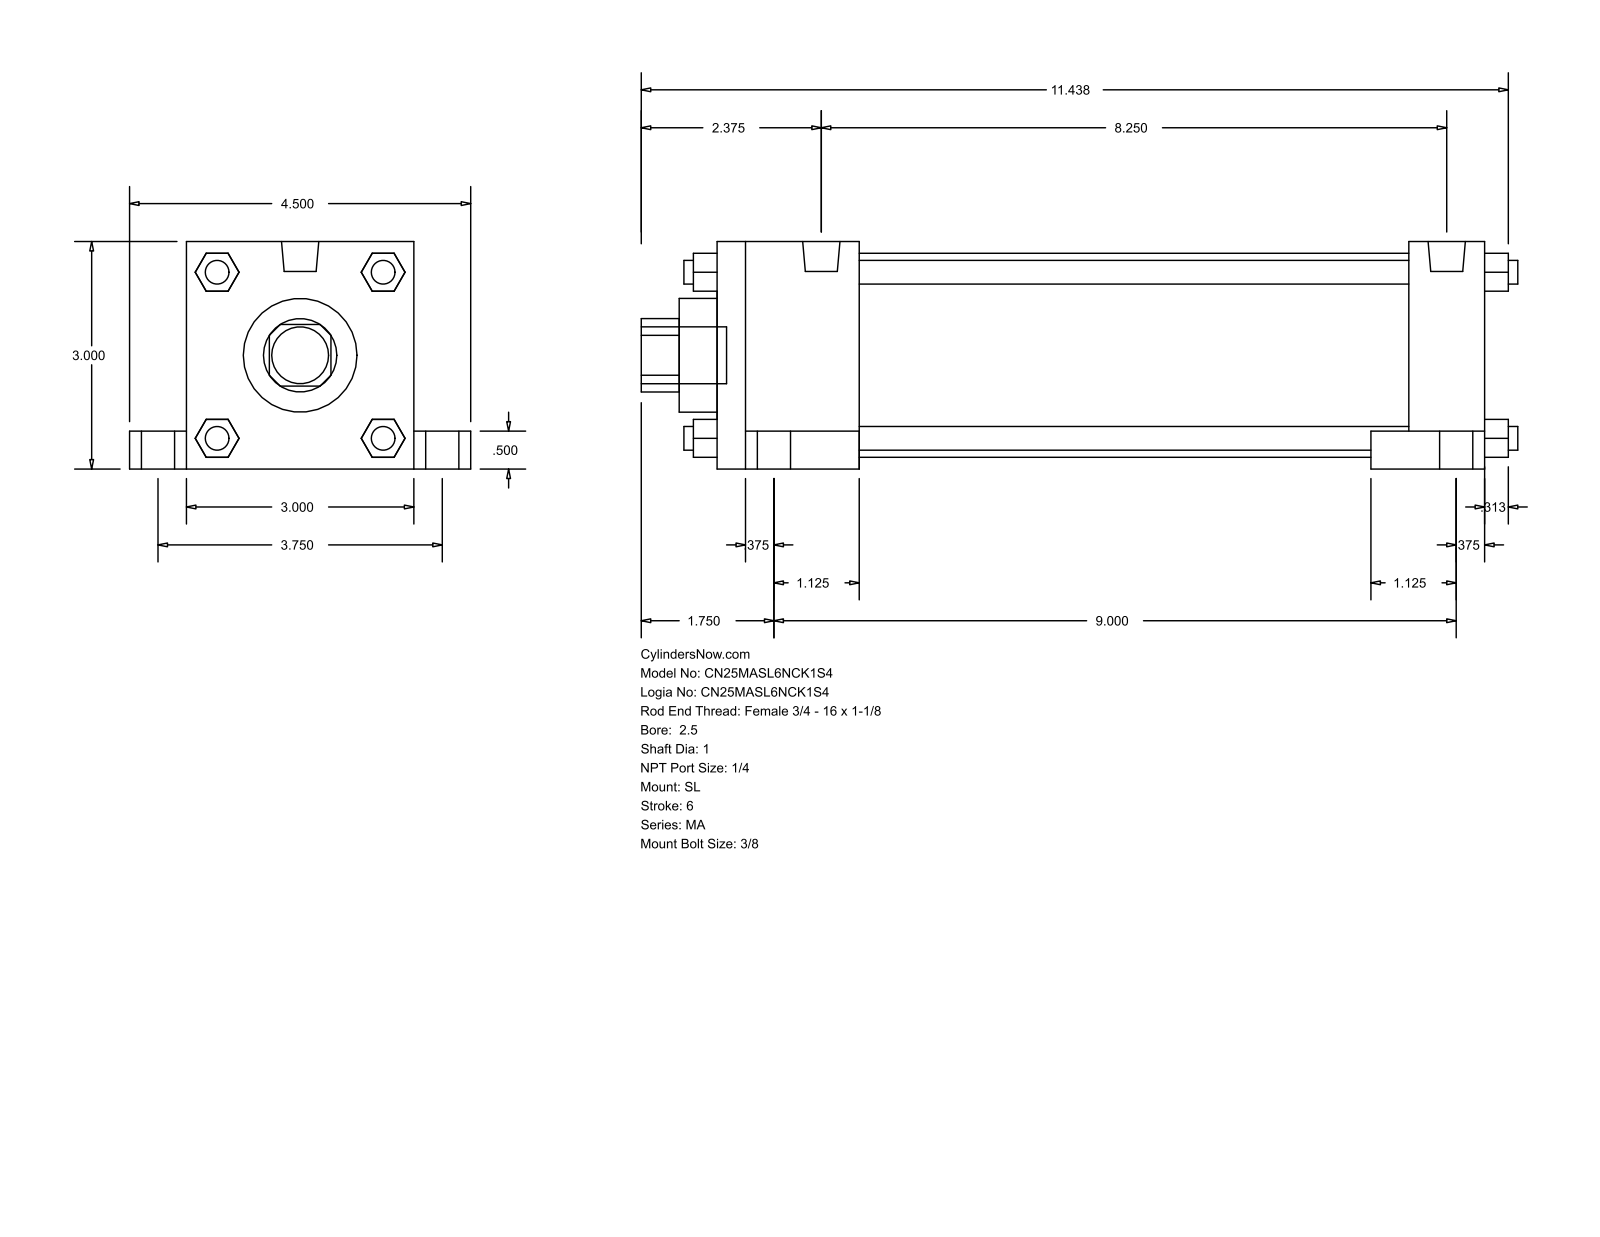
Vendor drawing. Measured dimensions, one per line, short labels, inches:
name: MA_SL__0250_1
written by: GSSL Pune (CONFIG_CONTROL_DESIGN)
unit: in
bodies: 0 solids, 148 faces (112 planar, 36 cylindrical, 0 other)
size: 11.563 × 4.5 × 3
holes: 1× ⌀1, 1× ⌀1.5, 1× ⌀2.69
bosses: 8× ⌀0.313, 4× ⌀0.687, 4× ⌀0.437, 2× ⌀0.492, 1× ⌀0.75
rounds: 1× R0.484
face distances: 3, 10.125, 0.5, 7.25, 1, 1.875, 8.25, 9.125, 0.75, 3.75
